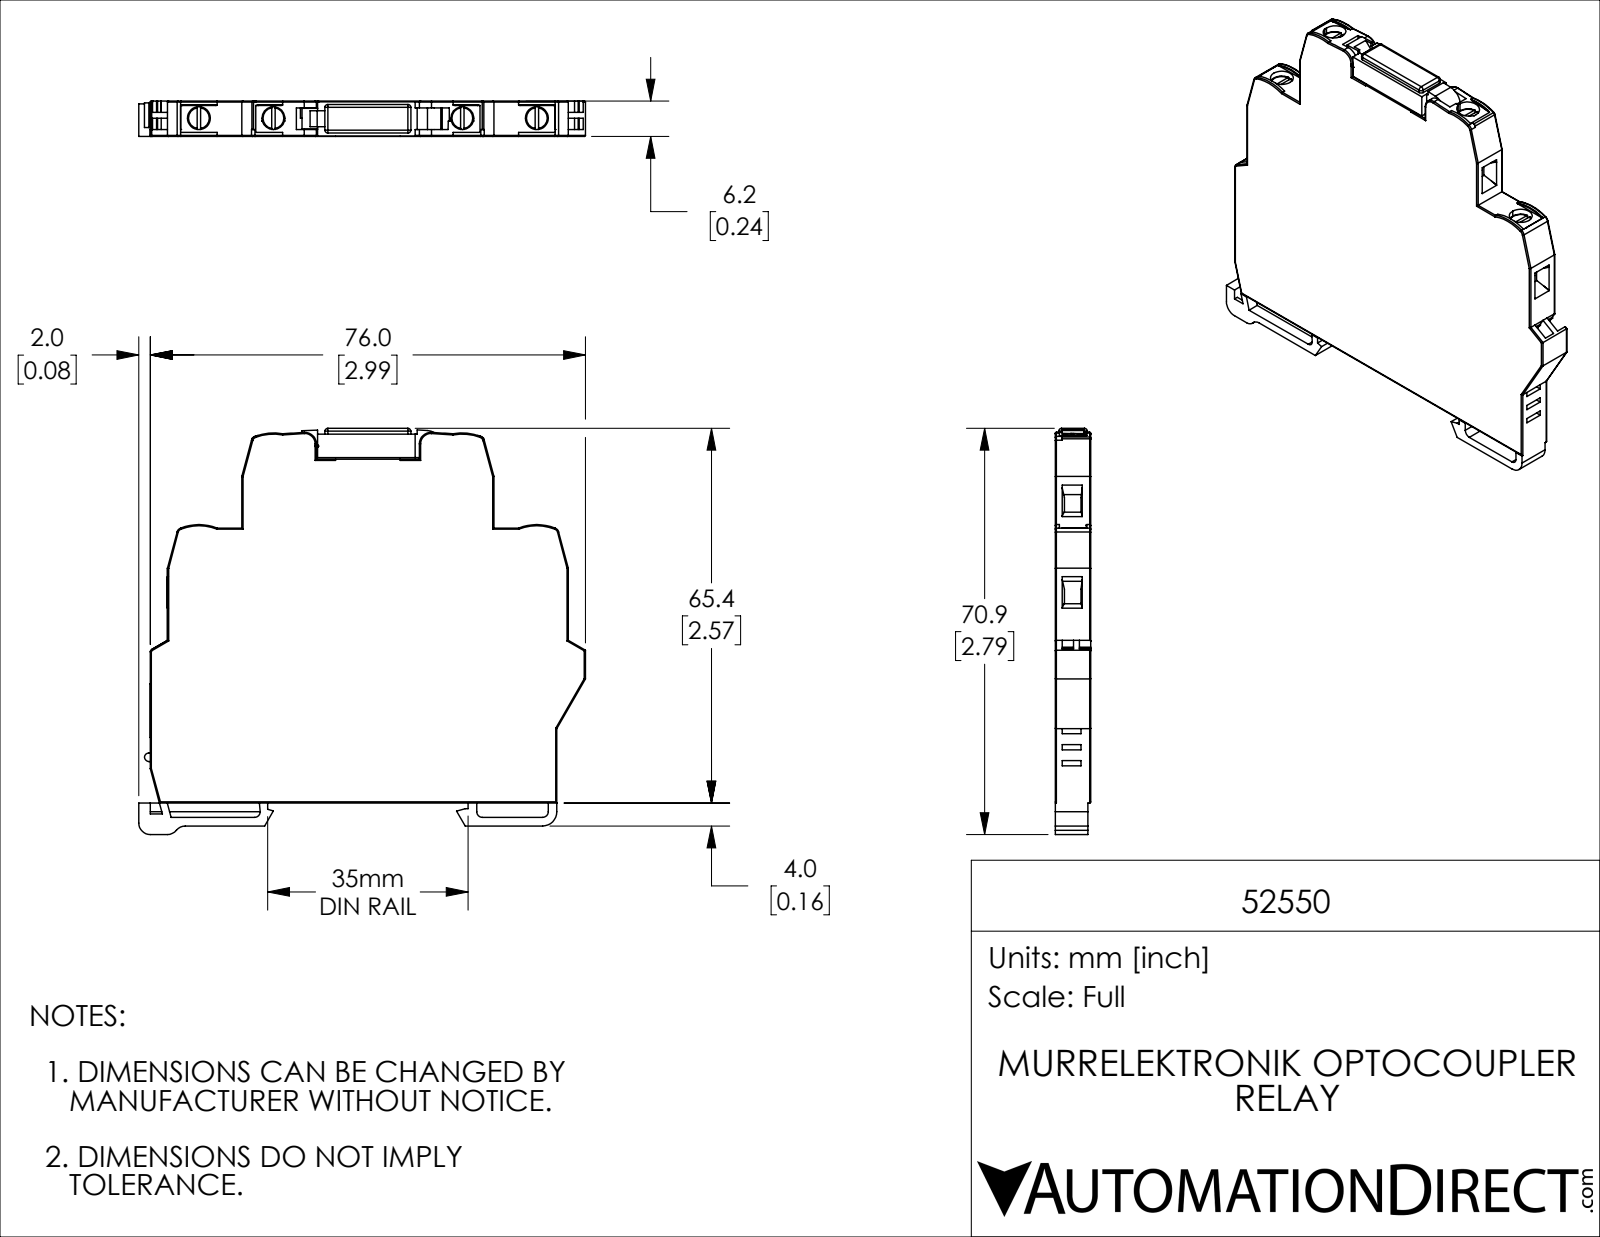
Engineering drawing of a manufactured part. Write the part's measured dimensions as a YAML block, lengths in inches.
part_name: "52550"
step_written_by: "SolidWorks 2019 (CONFIG_CONTROL_DESIGN)"
units: inches
bodies: {solids: 2, faces: 496, planar: 298, cylindrical: 138, other: 60}
overall_size: [3.071, 2.791, 0.244]
volume: 1.561
surface_area: 18.26
round_holes:
  - {diameter: 0.157, count: 4}
  - {diameter: 0.075, count: 1}
round_bosses_or_shafts:
  - {diameter: 0.079, count: 1}
partial_cylinders:
  - {radius: 0.008, count: 50}
  - {radius: 0.02, count: 11}
  - {radius: 0.039, count: 7}
  - {radius: 0.079, count: 6}
  - {radius: 0.03, count: 5}
  - {radius: 0.005, count: 4}
  - {radius: 0.346, count: 4}
  - {radius: 0.016, count: 3}
face_to_face_distances: [0.244, 0.059, 0.197, 0.118, 0.098, 2.362, 0.157, 0.079, 0.047, 0.02]
hole_center_spacings: [0.512, 1.811, 1.299, 2.323]
